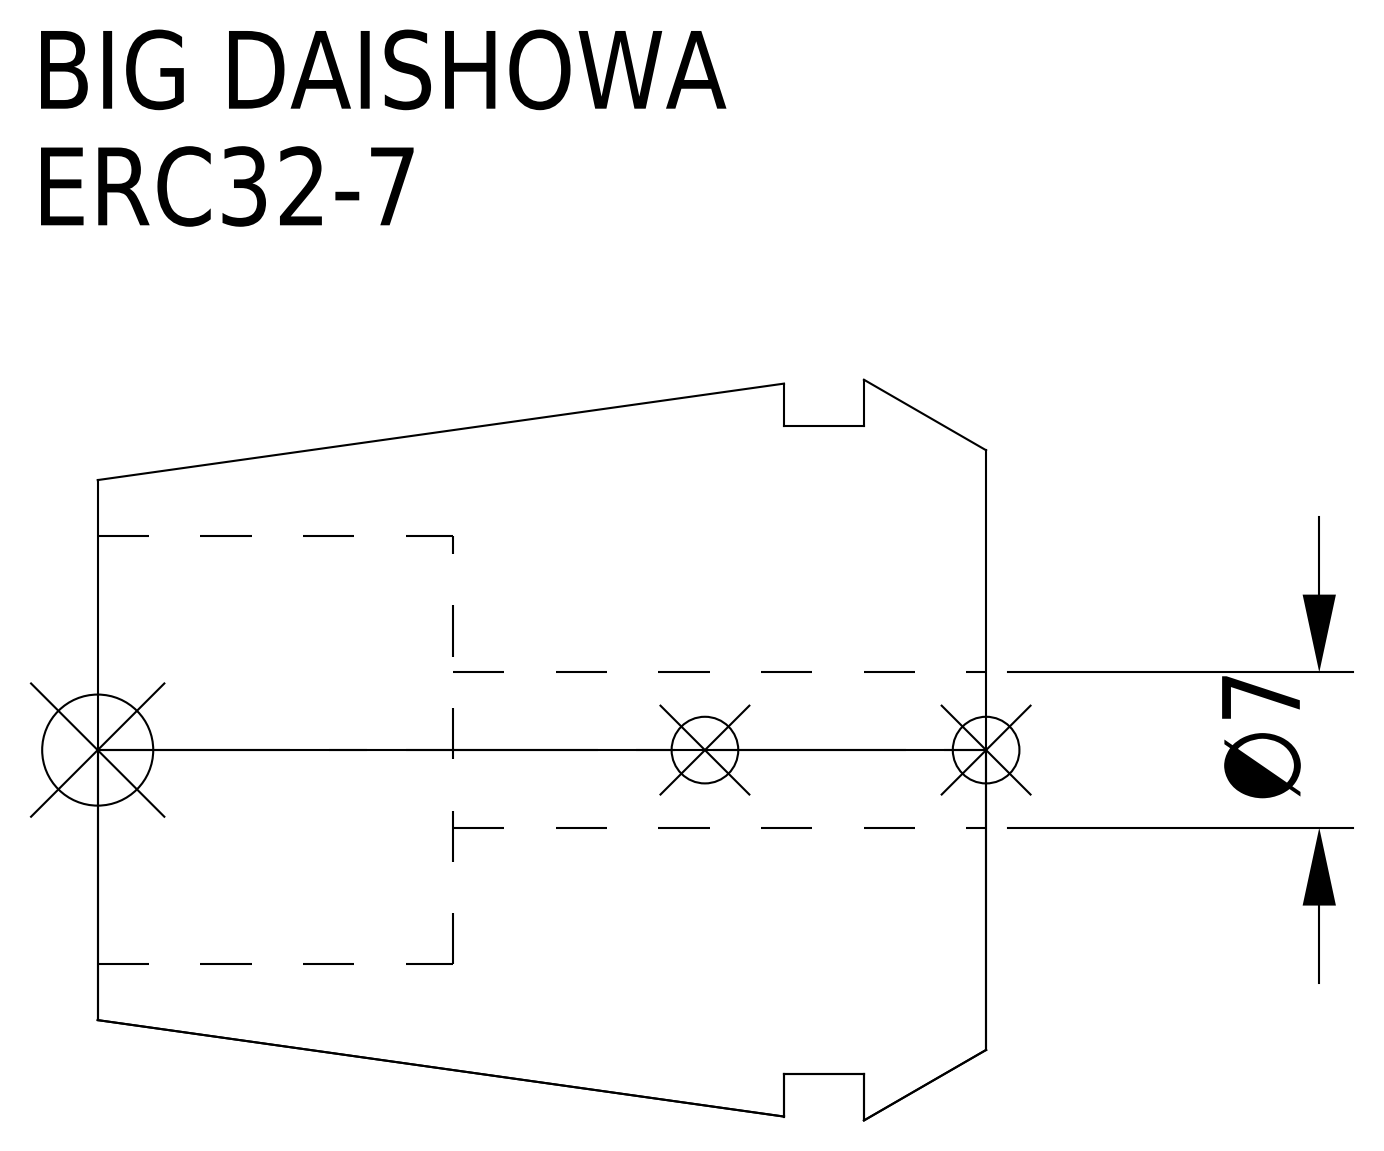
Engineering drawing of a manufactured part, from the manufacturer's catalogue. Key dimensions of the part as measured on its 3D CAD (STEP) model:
Part name (STEP PRODUCT): ERC32-7
STEP written by: CREO PARAMETRIC BY PTC INC, 2016380 (AUTOMOTIVE_DESIGN)
Units: millimetres
Bodies: 1 solid, 15 faces (5 planar, 6 cylindrical, 4 other)
Overall size (bounding box): 40 × 33.35 × 33.35
Volume: 20 838 mm³ · Surface area: 6 589 mm²
Round holes (diameter × count): ⌀7 ×1, ⌀19.3 ×1
Round bosses / shafts (diameter × count): ⌀29.2 ×1
Main face-to-face distances: 24, 5.5, 18.5, 9.1, 3.6, 14.9, 40, 34.5, 30.9, 16
